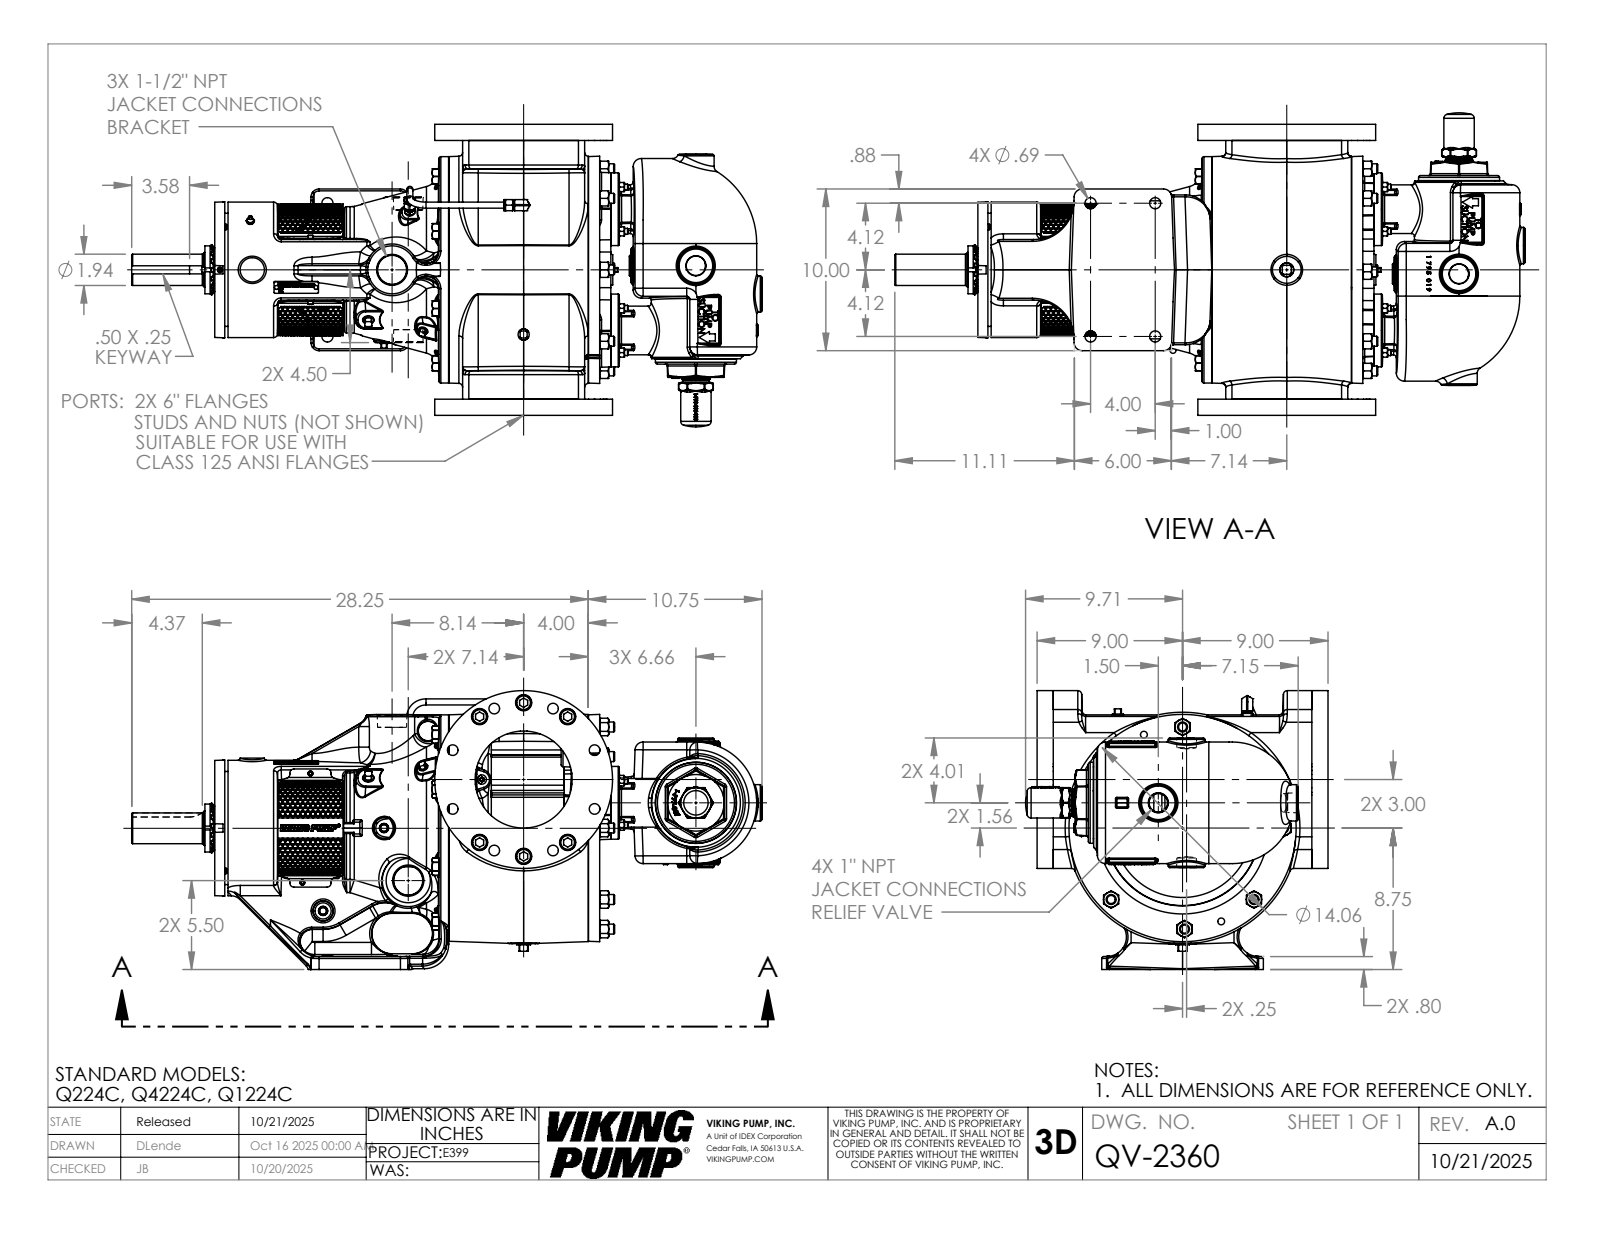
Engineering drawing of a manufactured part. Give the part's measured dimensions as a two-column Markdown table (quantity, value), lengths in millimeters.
| quantity | value |
| --- | --- |
| part name | QV-2360 |
| STEP written by | SolidWorks 2024 (AUTOMOTIVE_DESIGN) |
| units | millimeters |
| bodies | 1 solid, 5177 faces (1660 planar, 768 cylindrical, 2749 other) |
| overall size | 990.6 × 475.3 × 438.2 |
| volume | 55 140 000 mm³ |
| surface area | 1 789 000 mm² |
| round holes (diameter × count) | 6.4 × 9, 6.8 × 8, 16.7 × 8, 29.4 × 8, 25.4 × 7, 17.5 × 4, 22.2 × 4, 4 × 2, 8 × 2, 10.7 × 2, 11.5 × 1, 36.4 × 1 |
| round bosses / shafts (diameter × count) | 15.7 × 8, 9.4 × 8, 23.8 × 6, 9.5 × 5, 7.9 × 3, 4.8 × 3, 114.3 × 2, 17.4 × 2 |
| partial cylindrical surfaces (radius × count) | 3 × 60, 12.7 × 28, 1.5 × 26, 19.1 × 22, 0.4 × 18, 2.3 × 18, 1.8 × 16, 4.8 × 16 |
| main face-to-face distances | 25.4, 431.8, 457.2, 406.4, 14.5, 605, 97, 507.9, 565.6, 202.5 |
| hole center spacings | 95.3, 52.8, 120.7, 146.9, 68.9, 79.6, 96.2, 137.7 |
